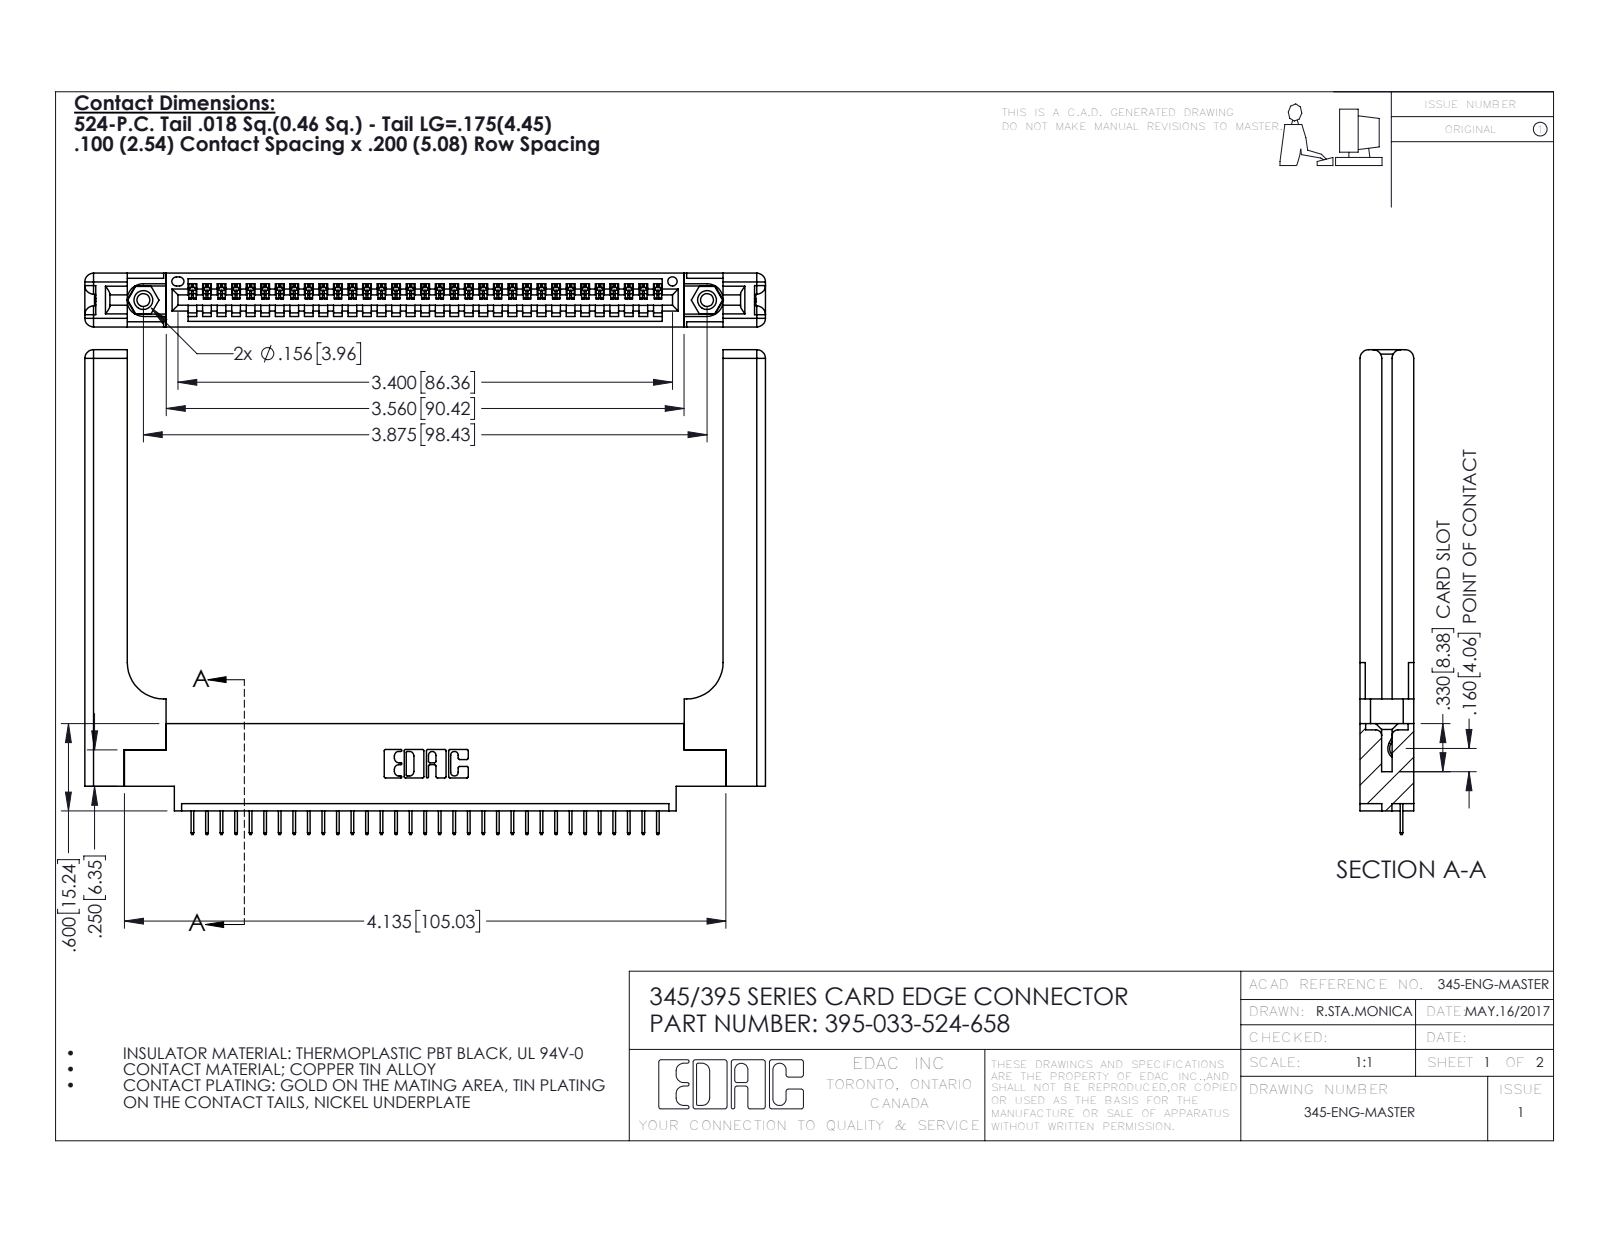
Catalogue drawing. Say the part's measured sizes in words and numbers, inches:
The part is named "345-292-001_345-293-124; 395-033-524-658; 345-250-001_345-250-001-102; 345-220-058_345-220-058 (+1 more)". Its 3-D file was written by "SolidWorks 2016 (CONFIG_CONTROL_DESIGN)". It is 38 solids with 2432 faces: 1750 planar, 622 cylindrical and 60 other. Overall it measures 4.679 by 3.332 by 0.37 inches. Its volume is 1.188 cubic inches and its surface area 30.18 square inches. Round holes: 2 of diameter 0.089, 2 of diameter 0.125, 2 of diameter 0.156, 1 of diameter 0.064. Round bosses or shafts: 2 of diameter 0.155. Partial cylindrical surfaces (rounded edges, fillets, slot ends): 66 of radius 0.006, 22 of radius 0.01, 16 of radius 0.06, 6 of radius 0.007, 6 of radius 0.031, 3 of radius 0.026, 2 of radius 0.03, 2 of radius 0.031. The main face-to-face distances are 0.37, 0.072, 0.298, 0.148, 0.15, 0.098, 0.272, 0.025, 0.2, 0.077. The hole center spacings are 0.27, 3.64, 3.875.
